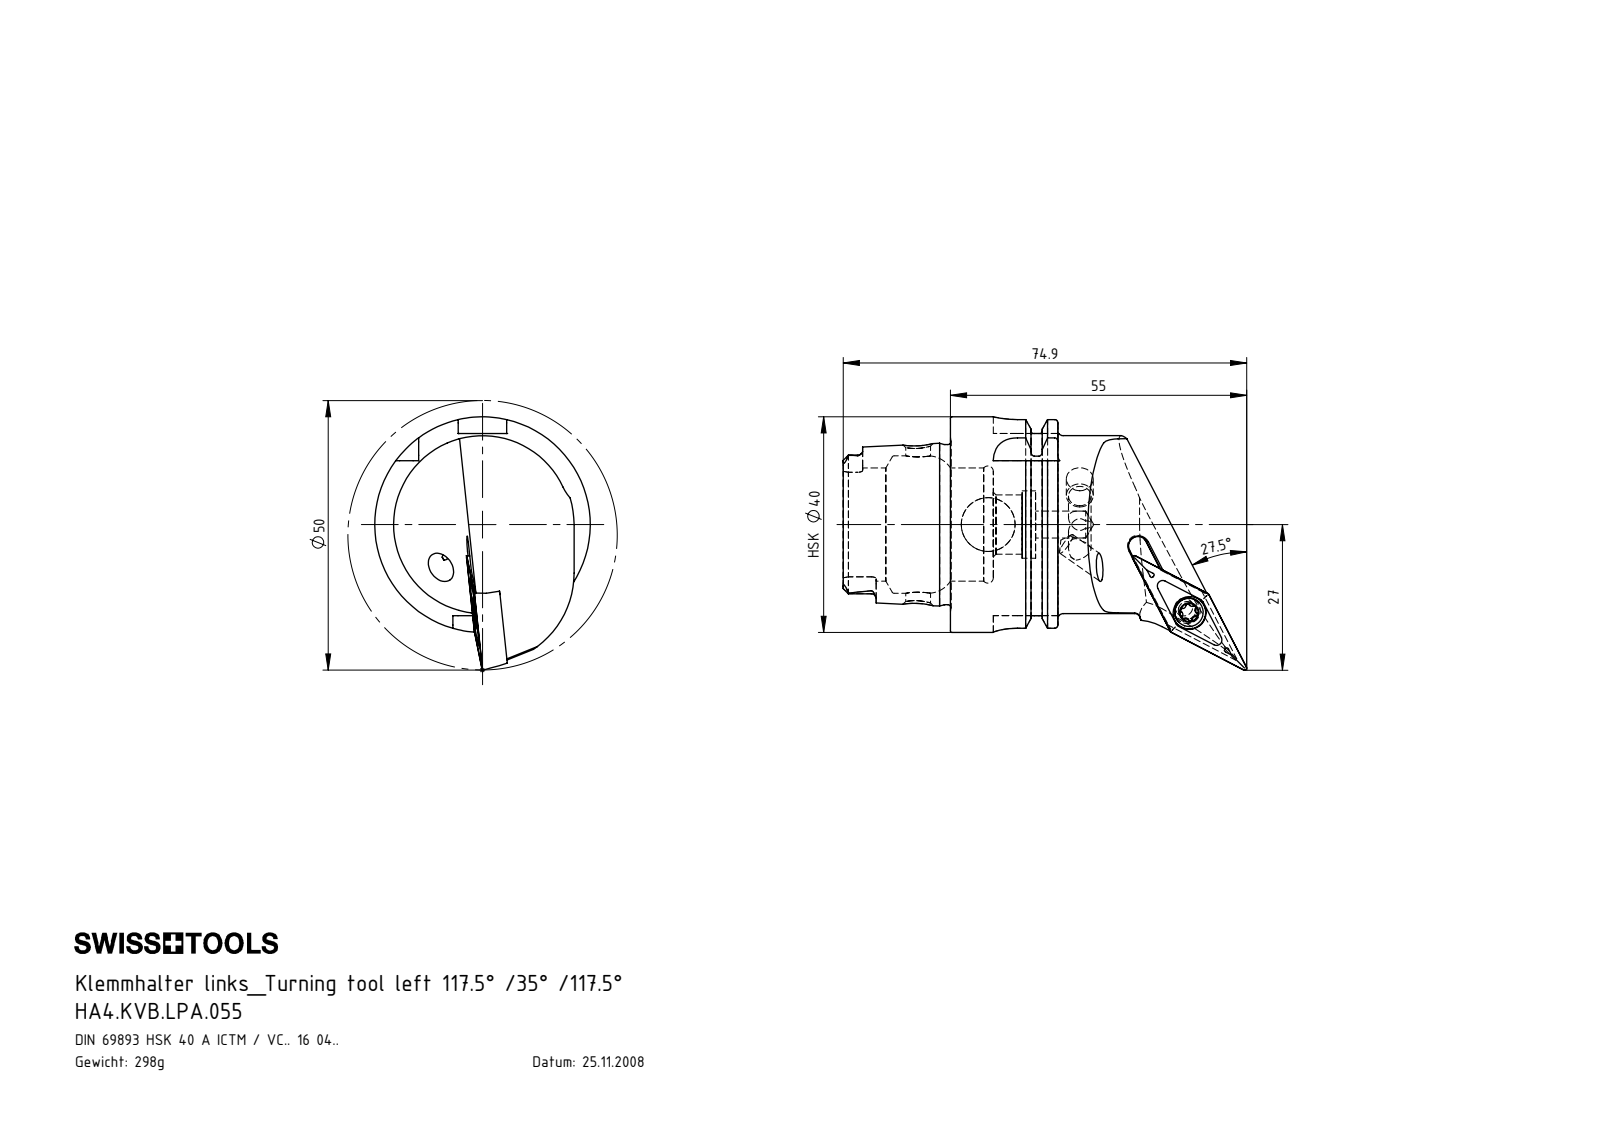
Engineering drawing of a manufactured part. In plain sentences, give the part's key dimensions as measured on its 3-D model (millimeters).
The part is named "HA4.KVB.LPA.055; VCMT160404; KVT_MB_600_050; WCB-ER2.001.009_A (+1 more)". Its 3-D file was written by "SolidWorks 2017 (AUTOMOTIVE_DESIGN)". It is 5 solids with 318 faces: 80 planar, 90 cylindrical and 148 other. Overall it measures 74.9 by 47 by 40 millimeters. Its volume is 37 478 cubic millimeters and its surface area 13 373 square millimeters. Round holes: 2 of diameter 4.2, 2 of diameter 5, 1 of diameter 3.3, 1 of diameter 4, 1 of diameter 4.4, 1 of diameter 4.6, 1 of diameter 6.1, 1 of diameter 10, 1 of diameter 11, 1 of diameter 12.5, 1 of diameter 21, 1 of diameter 25.5. Round bosses or shafts: 1 of diameter 40, 1 of diameter 34.75, 1 of diameter 33, 1 of diameter 29.71, 1 of diameter 5.25, 1 of diameter 5, 1 of diameter 4. Partial cylindrical surfaces (rounded edges, fillets, slot ends): 6 of radius 0.34, 6 of radius 0.59, 6 of radius 0.9, 4 of radius 4.5, 2 of radius 1.82, 2 of radius 1.88, 2 of radius 17, 1 of radius 1.75. The main face-to-face distances are 4.45, 7.95, 19.95, 12, 19.9, 27.85, 39.85, 35.7, 15.8, 7.85.
